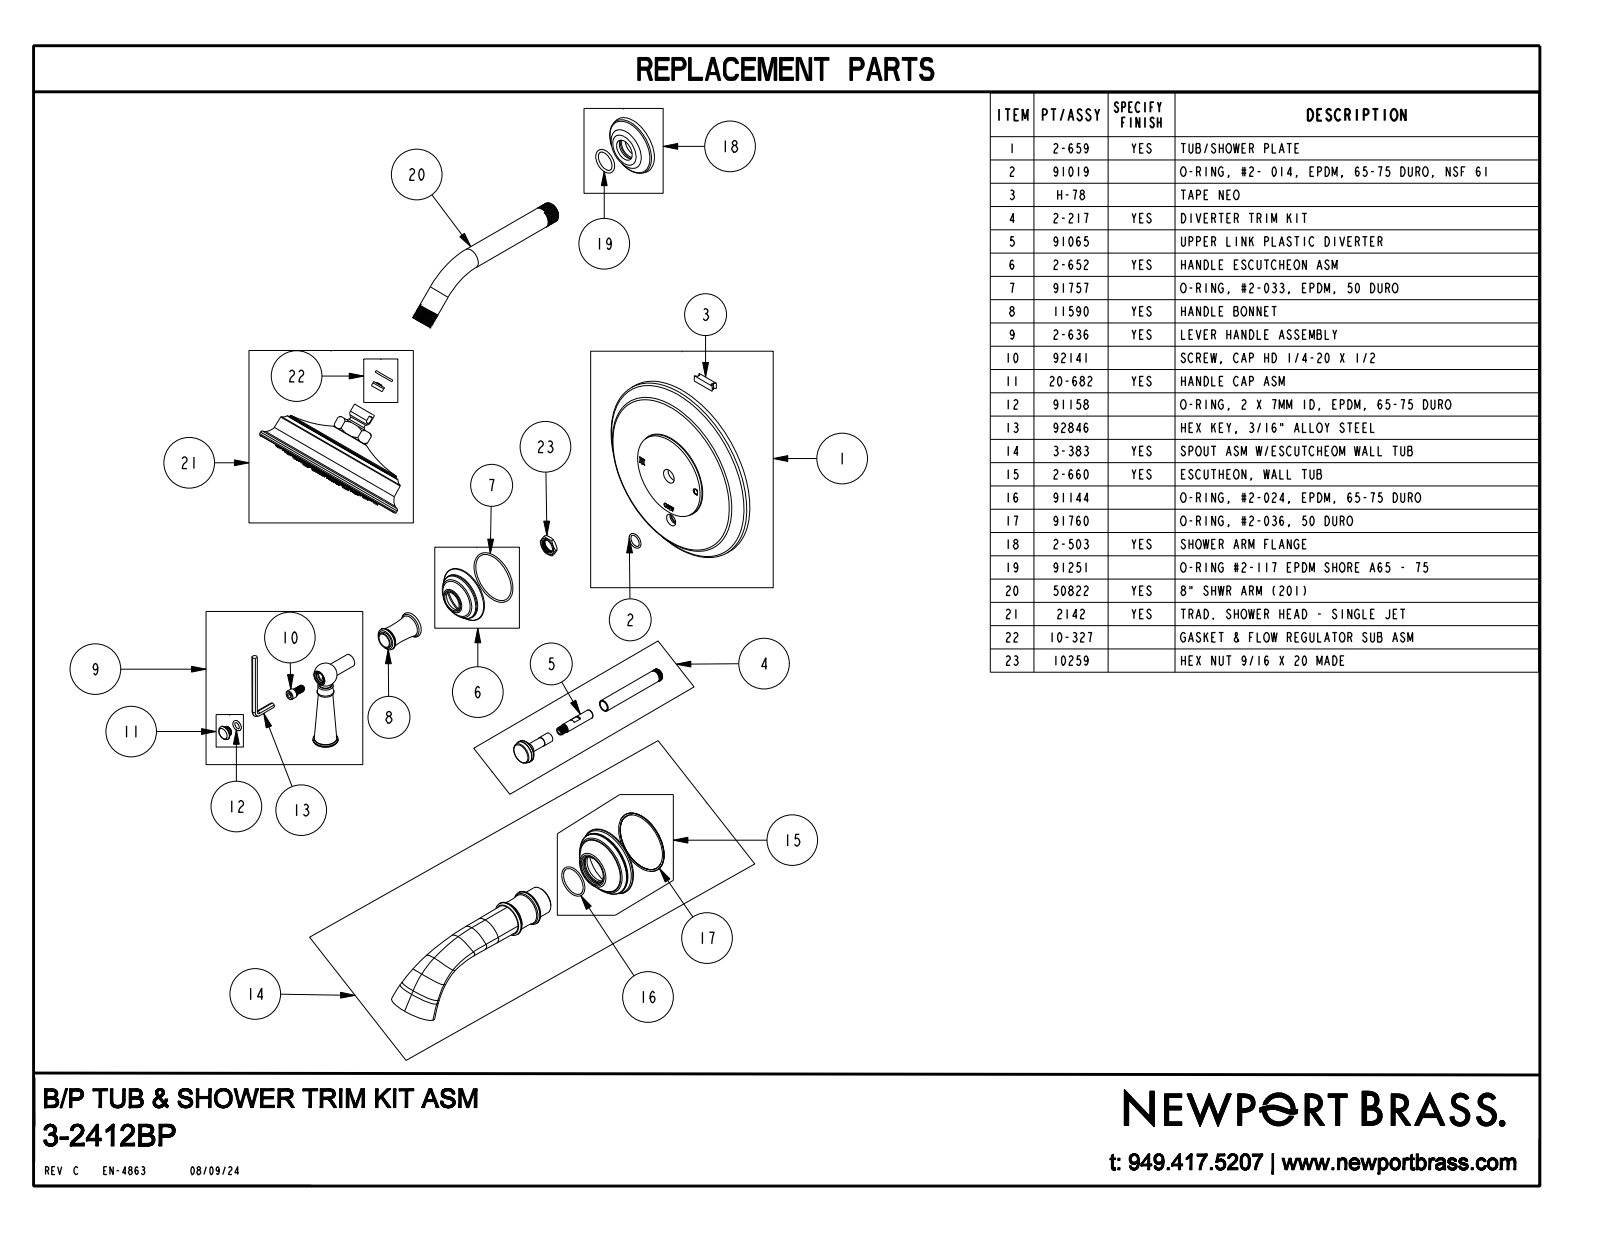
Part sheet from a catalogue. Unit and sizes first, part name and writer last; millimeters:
Units: millimetres
Overall size (bounding box): 532.7 × 271.6 × 190.5
Round holes (diameter × count): ⌀1.3 ×90, ⌀5.6 ×1, ⌀15.3 ×1, ⌀134 ×1
Round bosses / shafts (diameter × count): ⌀22.9 ×2, ⌀20.7 ×2, ⌀190.5 ×1, ⌀157.5 ×1, ⌀132.6 ×1, ⌀122.7 ×1, ⌀36.1 ×1, ⌀35.6 ×1
Main face-to-face distances: 15.9, 19.1, 3.2, 12.2, 3.7, 6.9, 25.8, 48.2, 36, 32.3
Hole centre spacings: 57.7, 12.2, 46.7, 24.2, 46.7, 35.8, 56.9, 66.1
Volume: 1 348 000 mm³ · Surface area: 180 900 mm²
Bodies: 3 solids, 1319 faces (277 planar, 238 cylindrical, 804 other)
Part name (STEP PRODUCT): 3-2412BP
STEP written by: CREO PARAMETRIC BY PTC INC, 2018400 (CONFIG_CONTROL_DESIGN)
